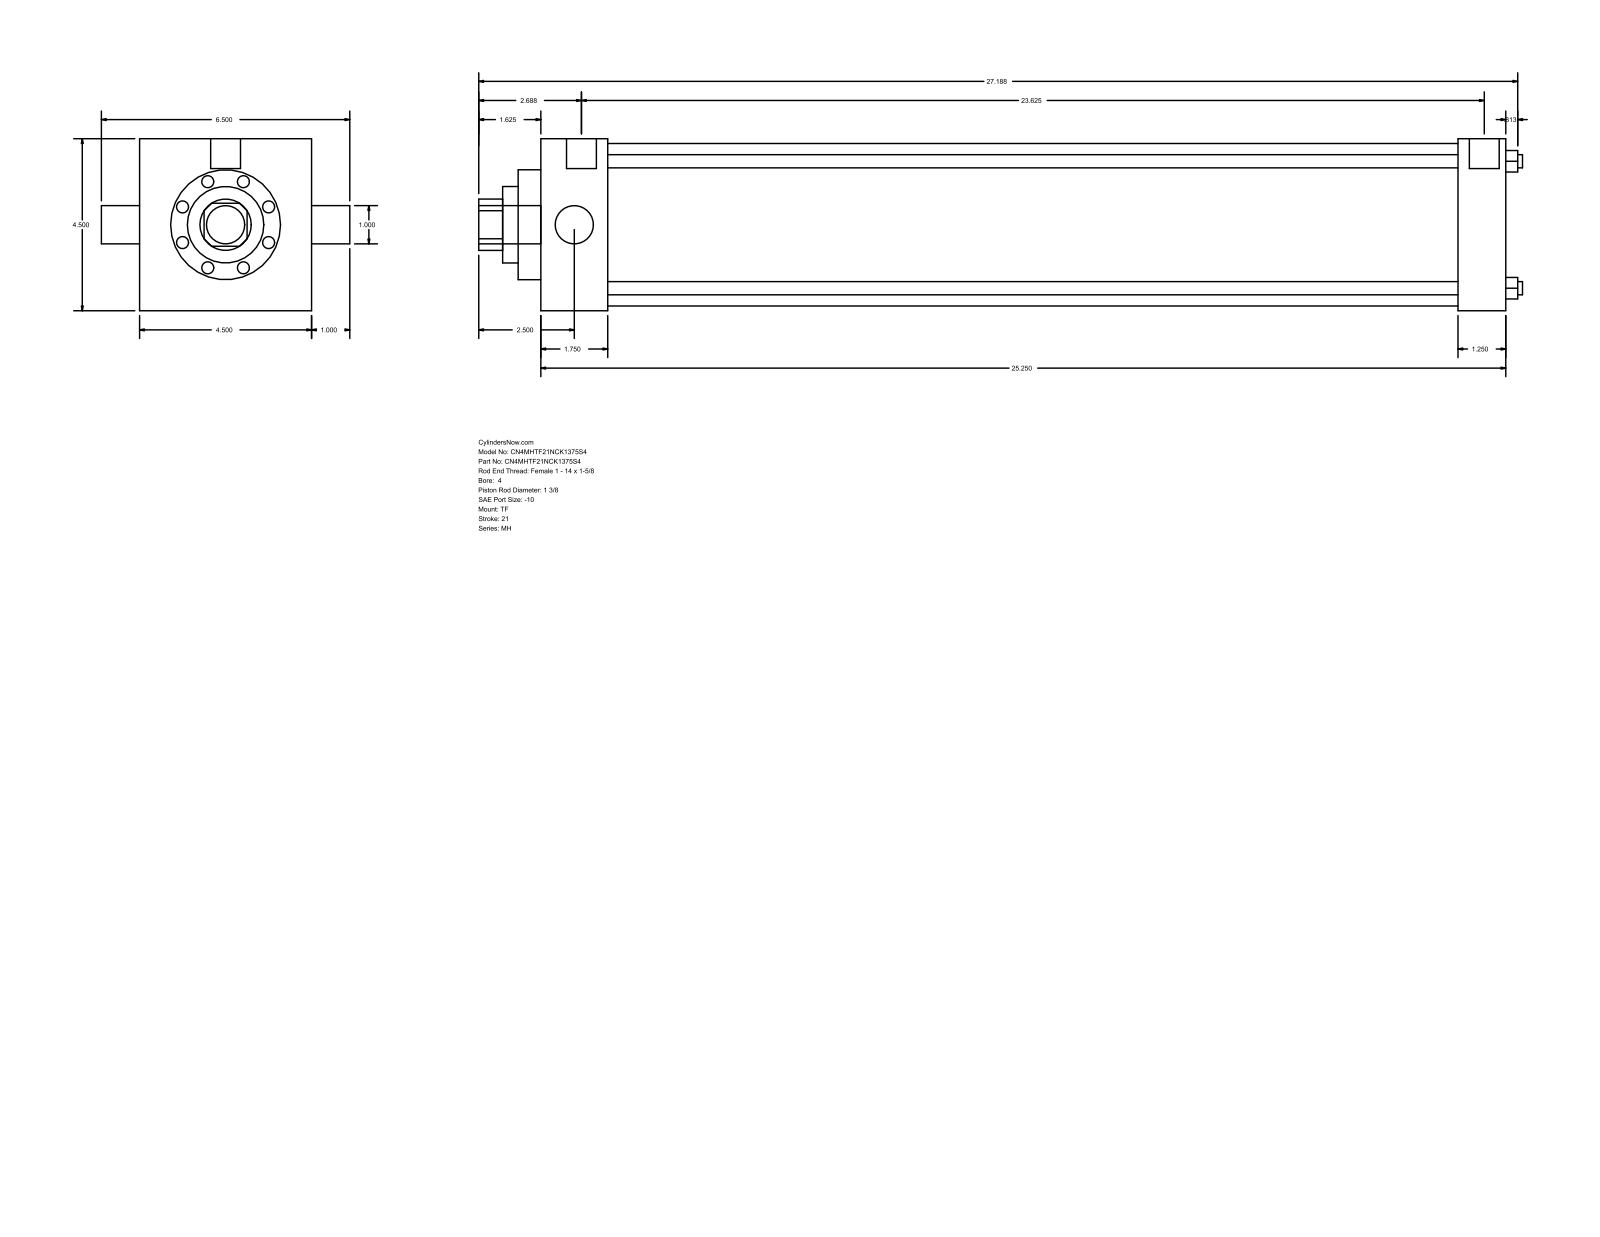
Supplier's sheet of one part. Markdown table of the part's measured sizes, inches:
| quantity | value |
| --- | --- |
| part name | MH_TF__0400_1.375 |
| STEP written by | GSSL Pune (CONFIG_CONTROL_DESIGN) |
| units | inches |
| bodies | 0 solids, 86 faces (61 planar, 25 cylindrical, 0 other) |
| overall size | 27.313 × 6.5 × 4.5 |
| round holes (diameter × count) | 0.345 × 4, 1 × 1, 1.375 × 1, 2 × 1, 2.875 × 1, 4.25 × 1 |
| round bosses / shafts (diameter × count) | 0.344 × 3, 0.781 × 2, 1 × 1 |
| partial cylindrical surfaces (radius × count) | 0.672 × 1 |
| main face-to-face distances | 4.5, 25.25, 1.75, 23.5, 24, 22.25, 1.25, 0.594, 2.344, 24.594 |
| hole center spacings | 2.347, 3.32, 4.695 |
